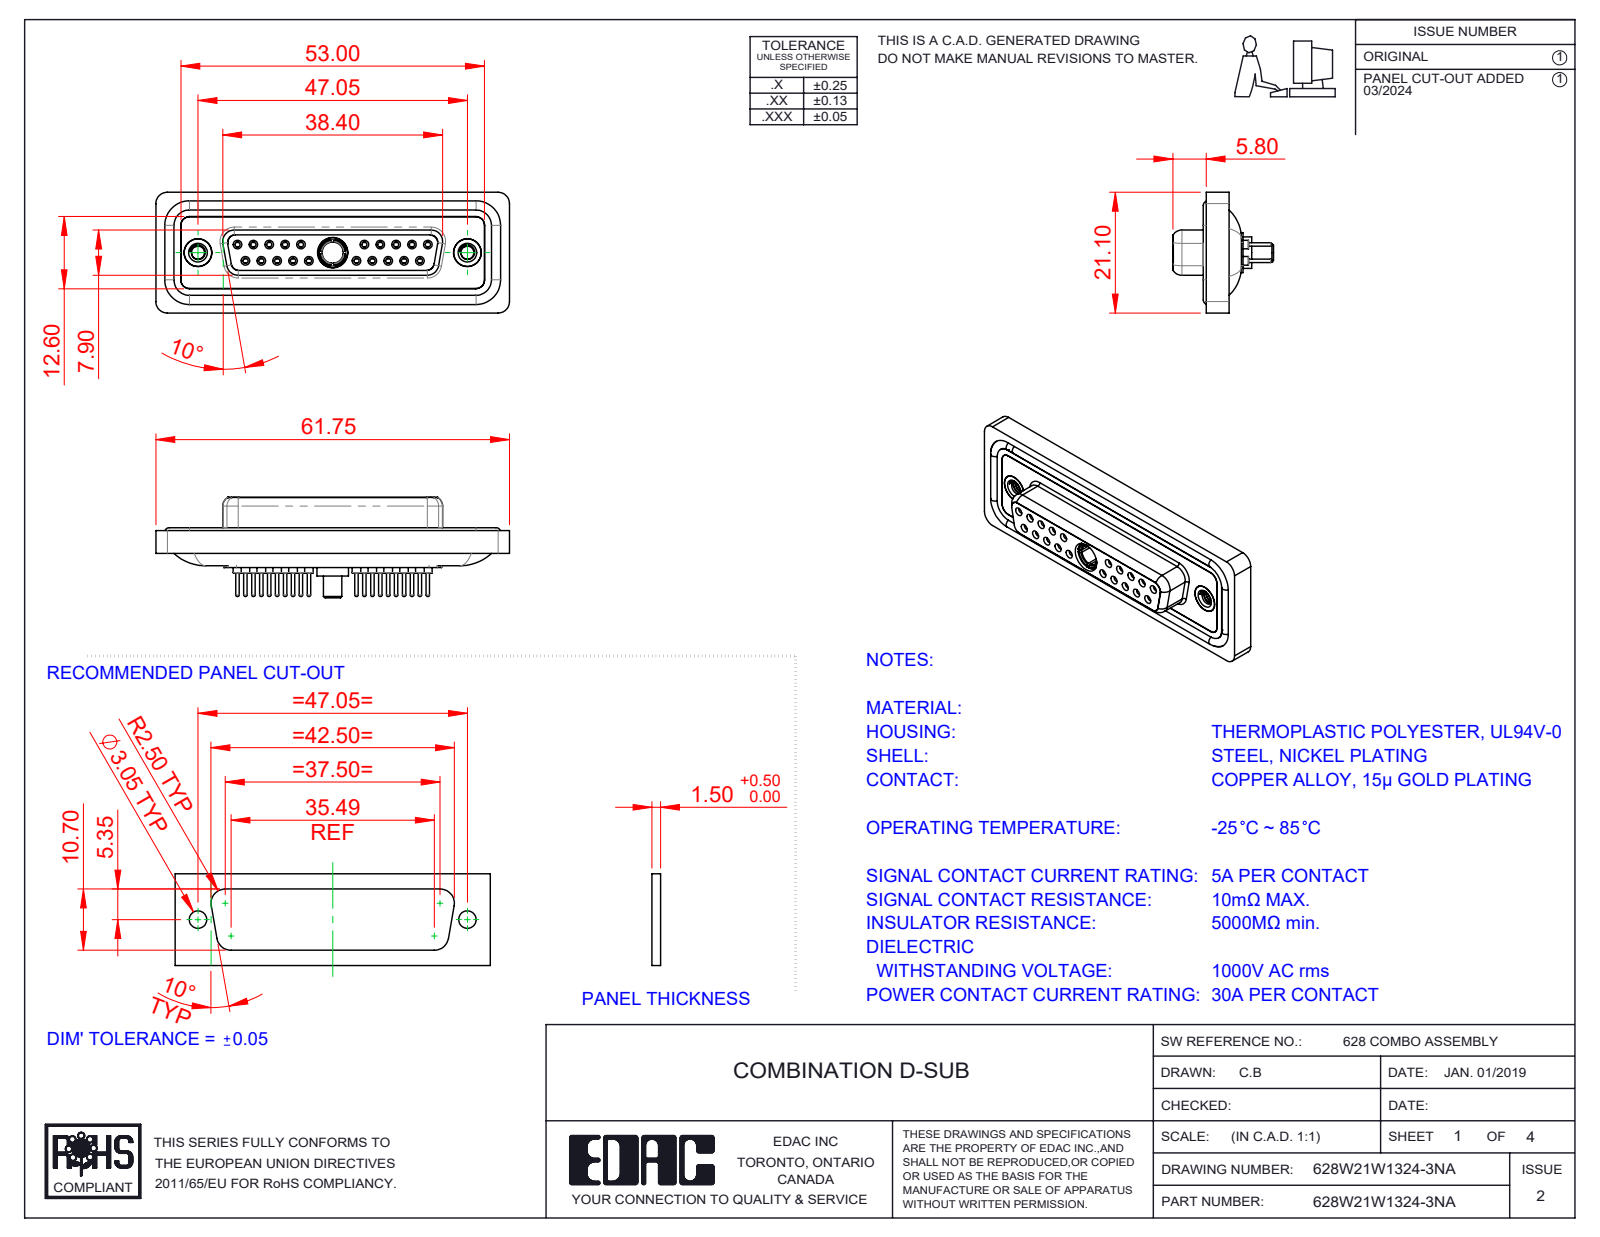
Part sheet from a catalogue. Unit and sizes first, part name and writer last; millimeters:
Units: millimetres
Overall size (bounding box): 61.75 × 21.1 × 17.55
Round holes (diameter × count): ⌀0.9 ×20, ⌀1.1 ×20, ⌀1.5 ×20, ⌀2 ×20, ⌀1.6 ×10, ⌀1.7 ×10, ⌀4.85 ×3, ⌀2.26 ×2, ⌀4 ×2, ⌀4.05 ×2, ⌀5 ×2, ⌀3.7 ×1
Round bosses / shafts (diameter × count): ⌀2.2 ×20, ⌀0.6 ×20, ⌀1.6 ×14, ⌀4.95 ×2, ⌀4.8 ×2, ⌀5.5 ×1, ⌀5.2 ×1, ⌀4.96 ×1
Partial cylindrical surfaces — rounded edges, fillets, slot ends (radius × count): R1.5 ×22, R2 ×18, R1.35 ×8, R1.6 ×8, R0.25 ×4, R0.5 ×4, R0.6 ×4, R0.65 ×4
Main face-to-face distances: 0.4, 1.8, 7.45, 6.6, 5.65, 0.5, 1.6, 7.05, 2.9, 1.1
Hole centre spacings: 3.16, 2.77, 5.54, 5.03, 8.31, 7.48, 16.62, 19.39
Volume: 8 383 mm³ · Surface area: 14 004 mm²
Bodies: 29 solids, 1558 faces (434 planar, 593 cylindrical, 531 other)
Part name (STEP PRODUCT): 628Combo Threaded Rivet_A; 628Combo Housing_21W1; 628Combo Shell Front_25 Contacts; Power Socket_30A S (+5 more)
STEP written by: SolidWorks 2023 (CONFIG_CONTROL_DESIGN)
